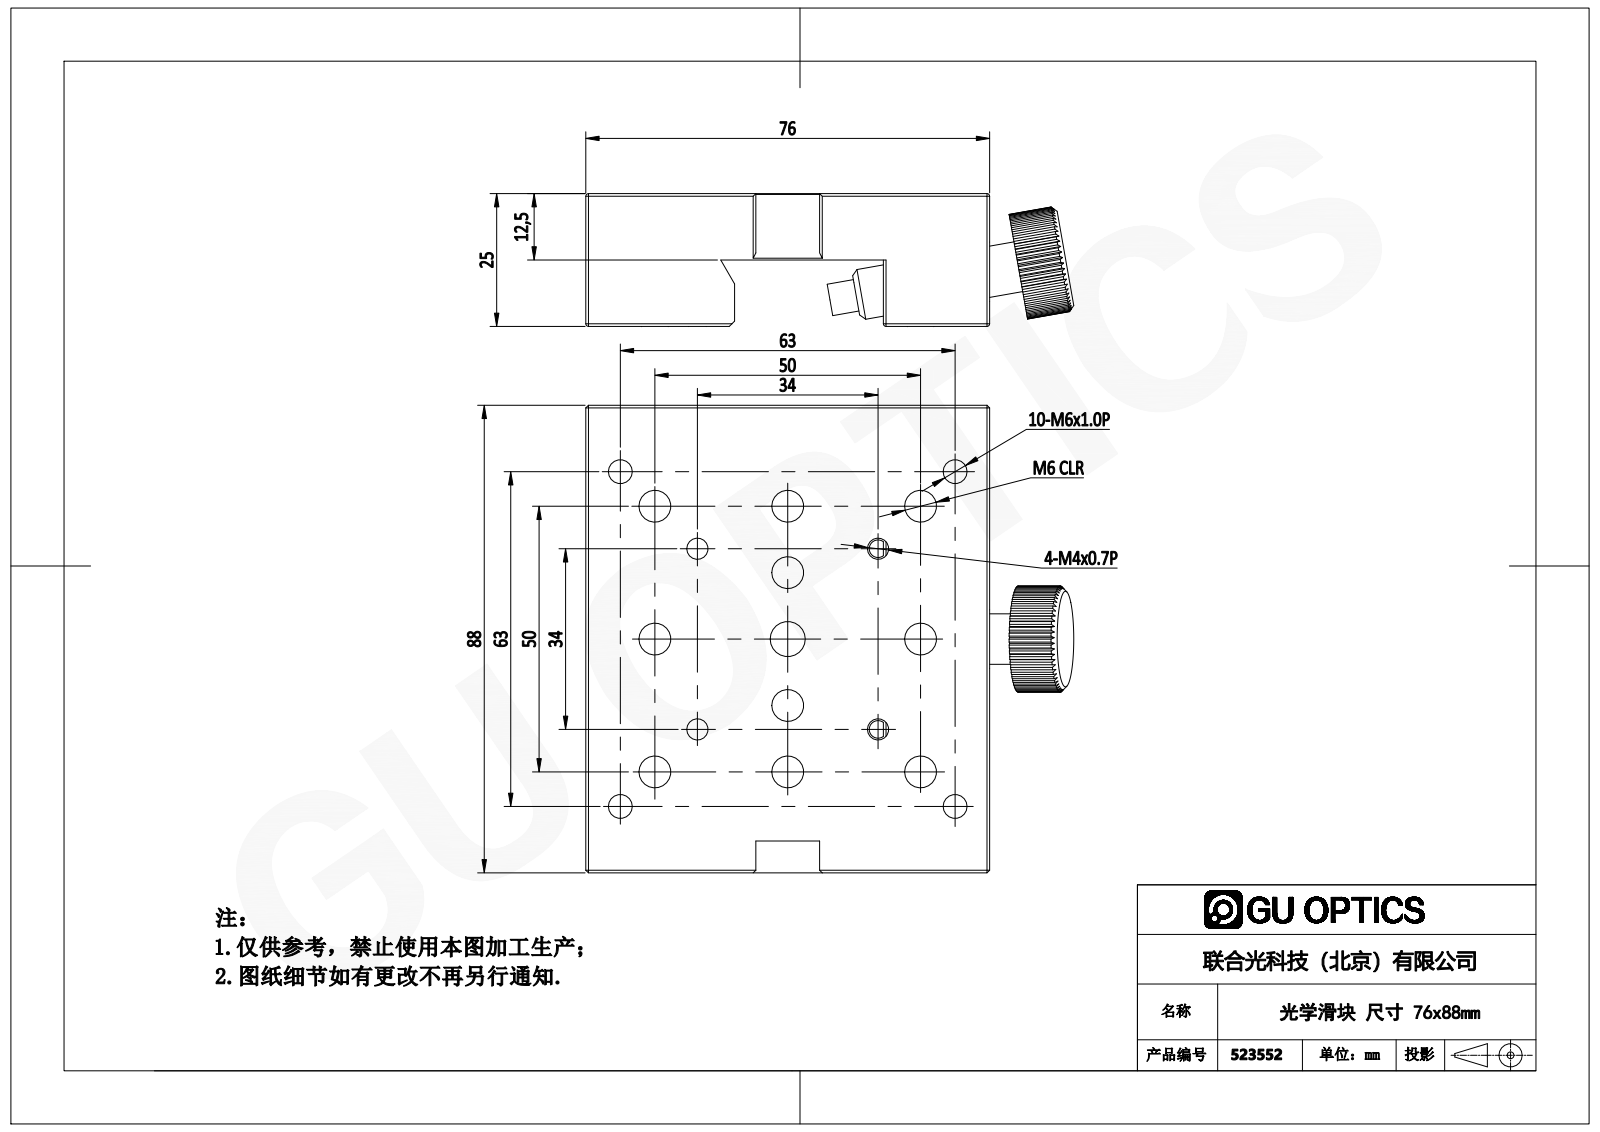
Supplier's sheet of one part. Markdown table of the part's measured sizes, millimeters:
| quantity | value |
| --- | --- |
| part name | CR-1 |
| STEP written by | SolidWorks 2012 (CONFIG_CONTROL_DESIGN) |
| units | millimeters |
| bodies | 0 solids, 264 faces (149 planar, 103 cylindrical, 12 other) |
| overall size | 91.83 × 88 × 25 |
| round holes (diameter × count) | 5 × 10, 6 × 10, 3.3 × 4, 4 × 4, 4.5 × 4, 7.5 × 4, 11 × 2, 6.5 × 1, 6.6 × 1 |
| round bosses / shafts (diameter × count) | 9.5 × 1, 6 × 1 |
| partial cylindrical surfaces (radius × count) | 0.5 × 5, 10 × 1 |
| main face-to-face distances | 12.5, 25, 76, 88, 28, 56, 20, 48, 9, 9.5 |
| hole center spacings | 25, 18.79, 27.95, 32.16, 35.36, 42.76, 45.31, 50.62 |
